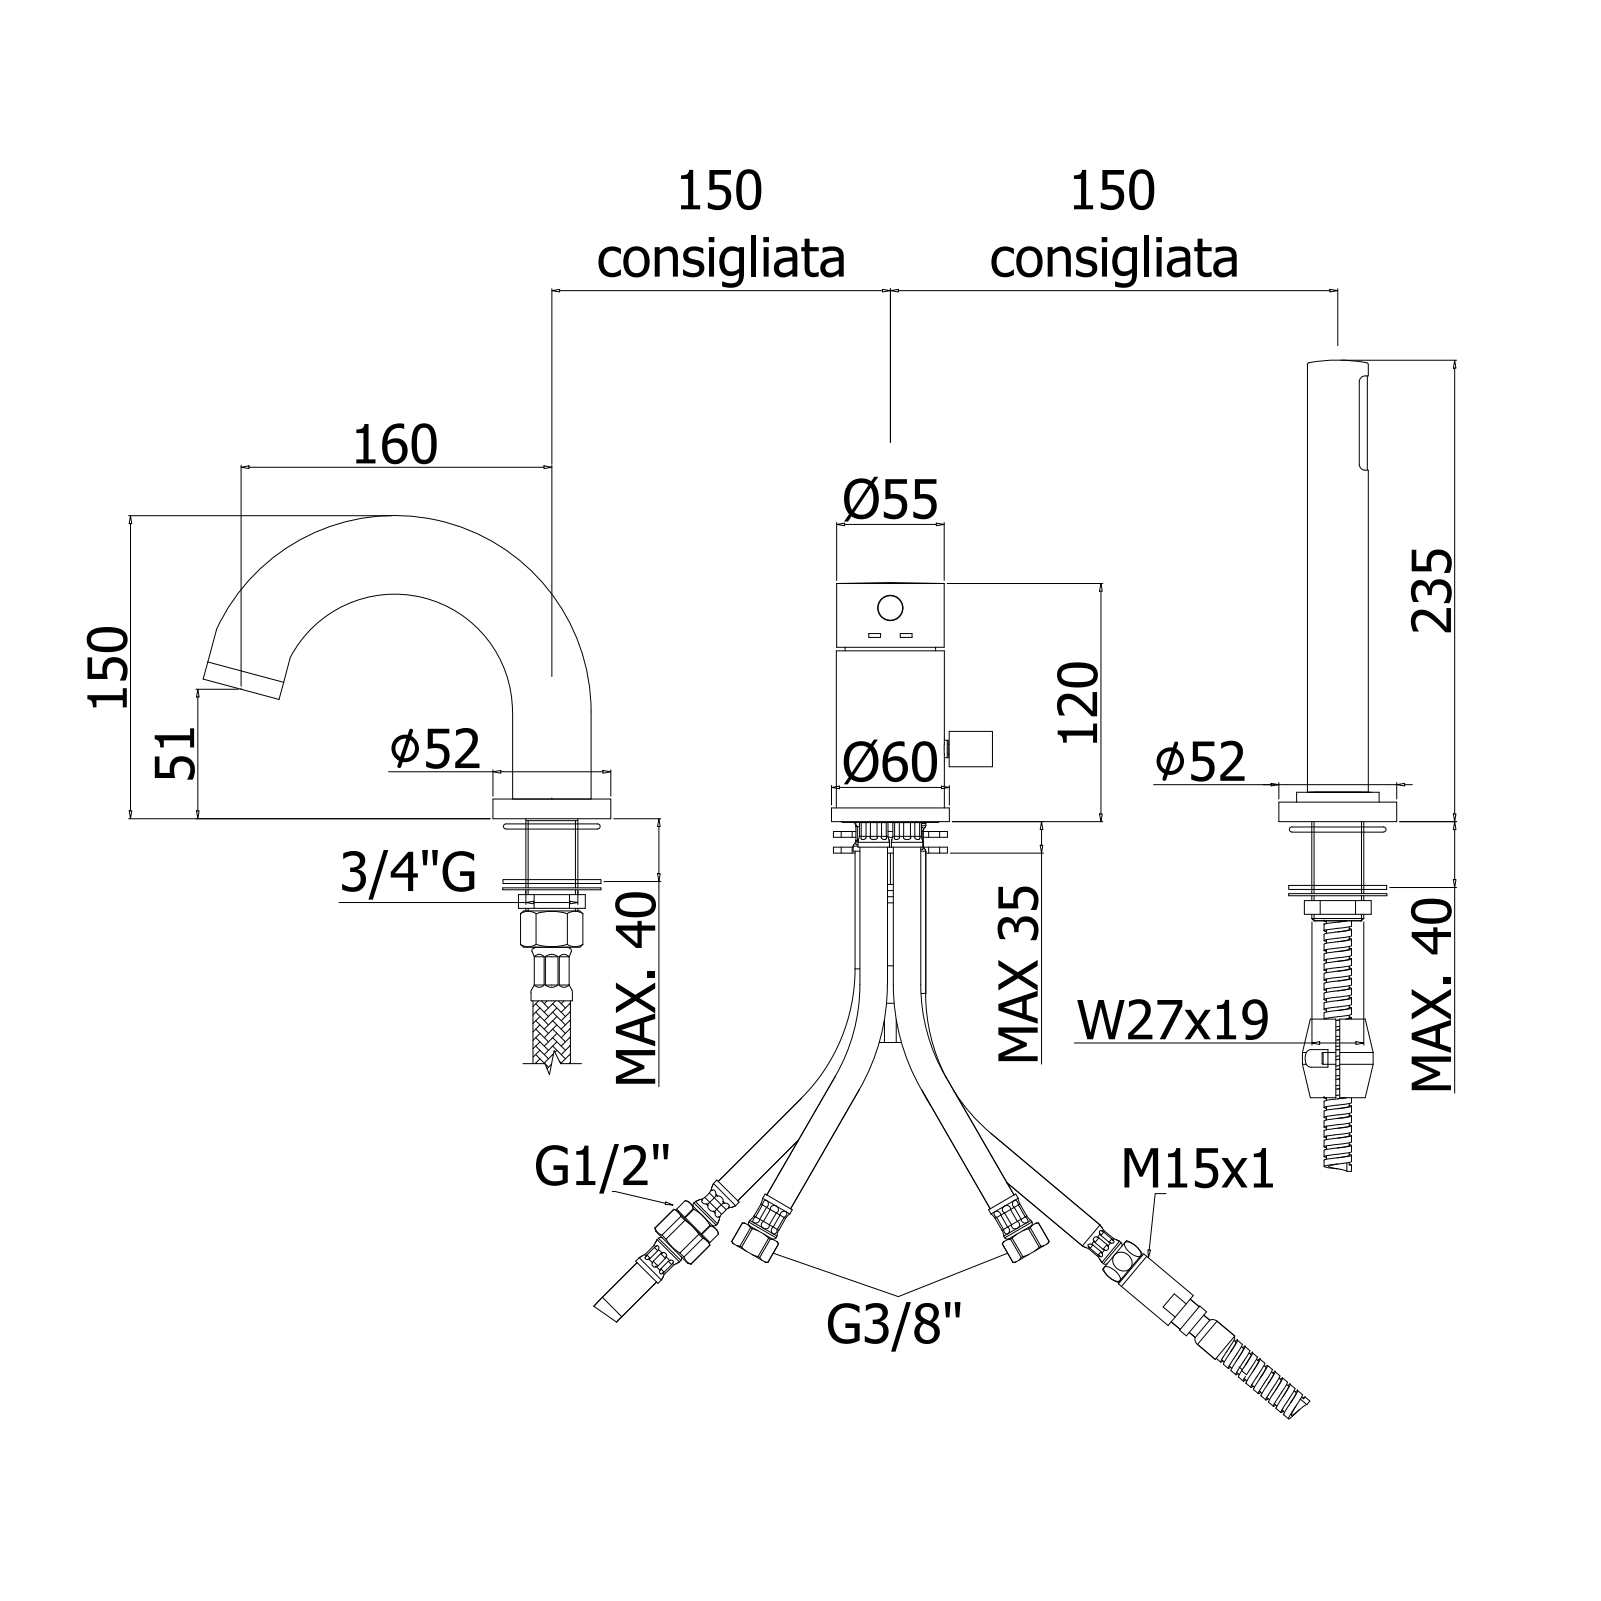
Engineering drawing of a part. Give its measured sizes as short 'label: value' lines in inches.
name: SK047CR
written by: CREO PARAMETRIC BY PTC INC, 2020044 (CONFIG_CONTROL_DESIGN)
unit: in
bodies: 5 solids, 254 faces (78 planar, 108 cylindrical, 68 other)
size: 15.827 × 8.74 × 8.261
volume: 42.14 in³; area: 197.7 in²
holes: 4× ⌀0.315, 4× ⌀0.433, 4× ⌀0.512, 2× ⌀0.217, 2× ⌀0.394, 1× ⌀0.197, 1× ⌀0.276, 1× ⌀0.354, 1× ⌀0.496, 1× ⌀0.506, 1× ⌀0.644, 1× ⌀0.669
bosses: 2× ⌀2.047, 2× ⌀1.417, 1× ⌀2.362, 1× ⌀2.165, 1× ⌀2.154, 1× ⌀1.87, 1× ⌀1.654, 1× ⌀1.26
rounds: 1× R0.217, 1× R0.236, 1× R0.394, 1× R0.524, 1× R1.081
face distances: 3.42, 0.276, 3.425, 3.15, 3.811, 4.087, 0.661, 0.271, 4.082, 2
hole spacings: 0.088, 0.487, 0.488, 0.535, 0.535, 0.568, 0.585, 0.614
